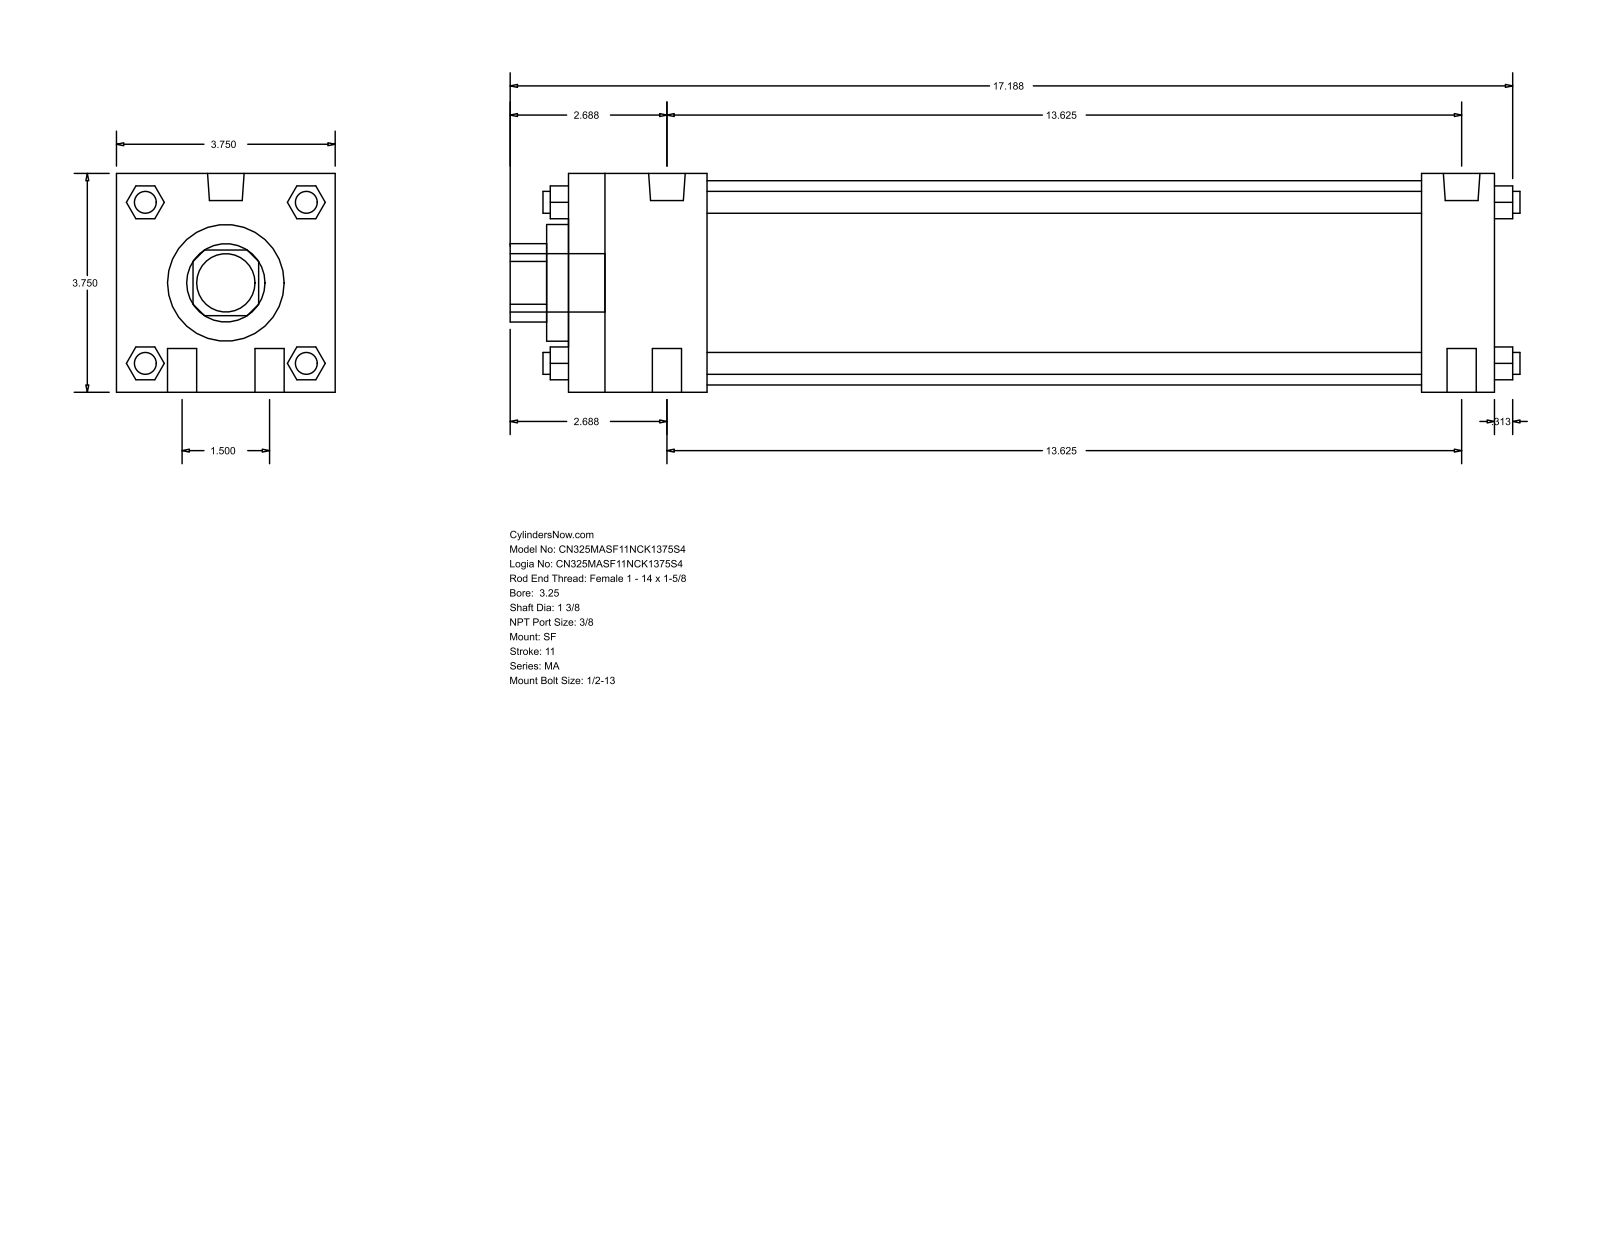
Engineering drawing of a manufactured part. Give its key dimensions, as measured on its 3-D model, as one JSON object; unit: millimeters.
{"part_name": "MA_SF__0325_1.375", "step_written_by": "GSSL Pune (CONFIG_CONTROL_DESIGN)", "units": "millimeters", "bodies": {"solids": 0, "faces": 124, "planar": 94, "cylindrical": 30, "other": 0}, "overall_size": [439.74, 95.25, 95.25], "round_holes": [[34.92, 1], [50.8, 1], [88.9, 1]], "round_bosses_or_shafts": [[12.7, 4], [9.53, 4], [15.93, 2], [11.11, 2], [25.4, 1]], "partial_cylinders_radius": [[17.06, 1]], "face_to_face_distances": [95.24, 403.22, 371.48, 31.74, 60.32, 311.16, 342.9, 9.52, 69.84, 381]}
